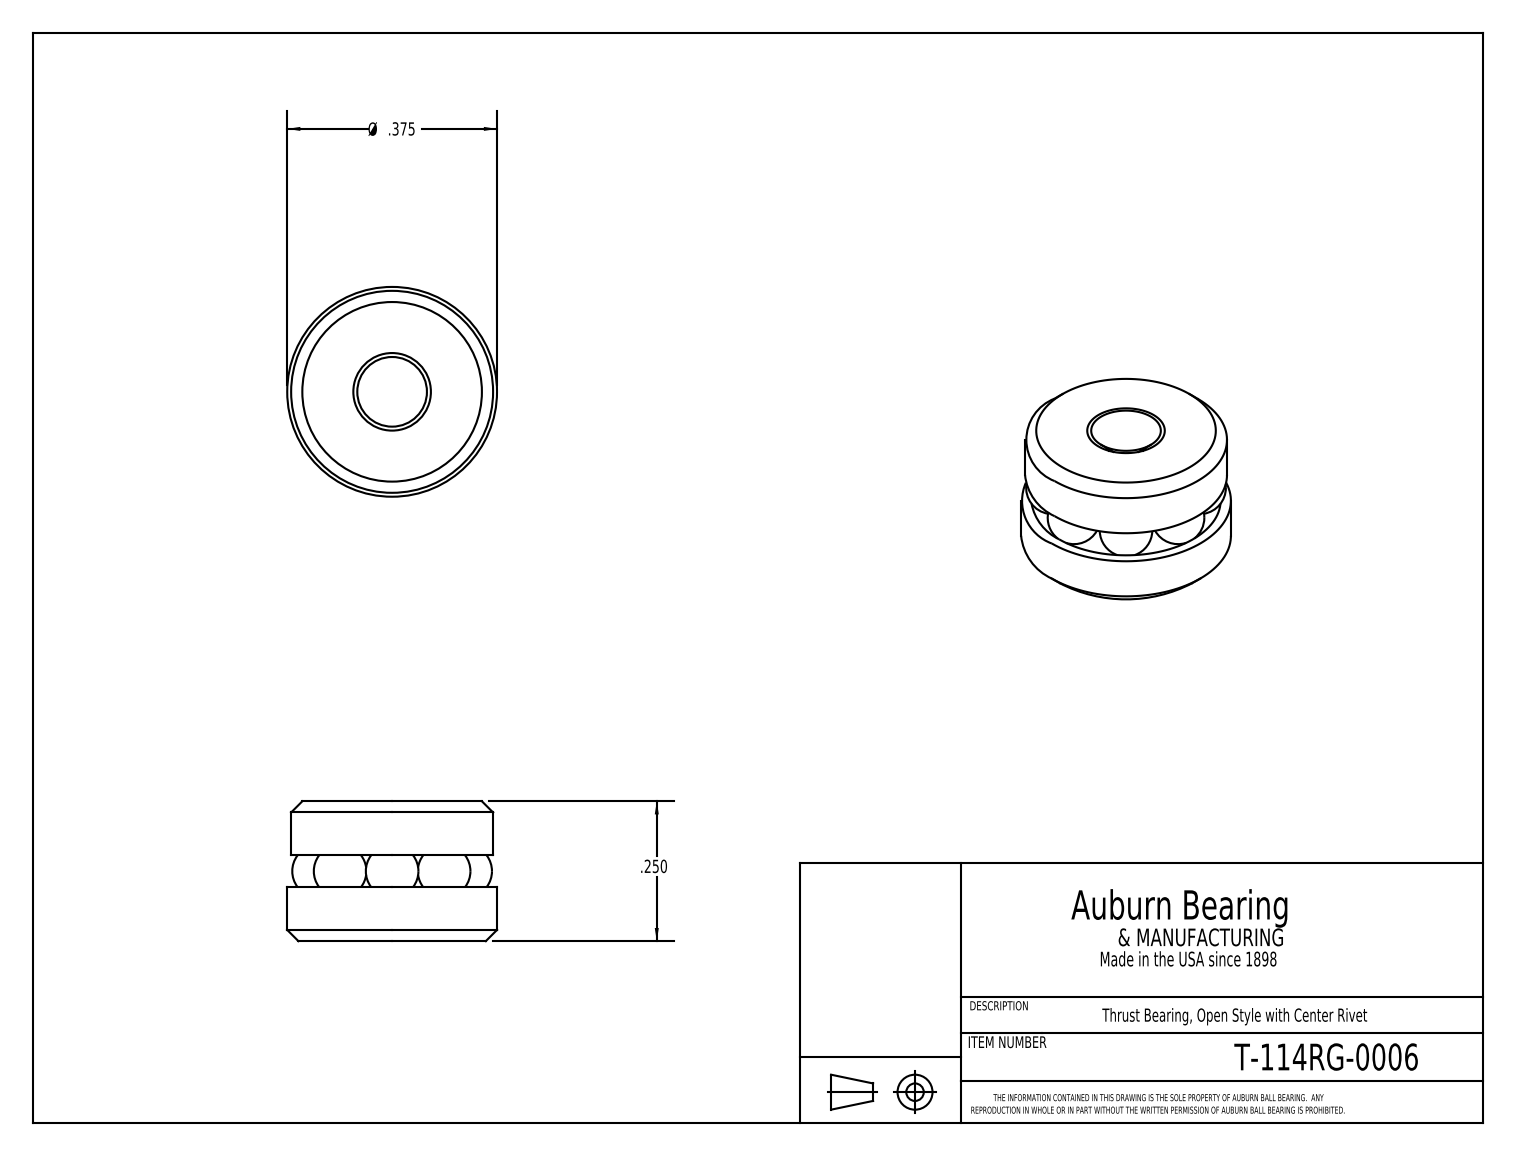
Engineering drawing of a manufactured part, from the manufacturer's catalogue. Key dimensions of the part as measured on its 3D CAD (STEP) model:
Part name (STEP PRODUCT): T-114RG_T-114RG-0006
STEP written by: SolidWorks 2016 (CONFIG_CONTROL_DESIGN)
Units: inches
Bodies: 11 solids, 29 faces (8 planar, 5 cylindrical, 16 other)
Overall size (bounding box): 0.375 × 0.375 × 0.25
Volume: 0.022 in³ · Surface area: 0.971 in²
Round holes (diameter × count): ⌀0.072 ×1
Round bosses / shafts (diameter × count): ⌀0.375 ×1, ⌀0.361 ×1, ⌀0.062 ×1
Main face-to-face distances: 0.097, 0.153, 0.25, 0.056
